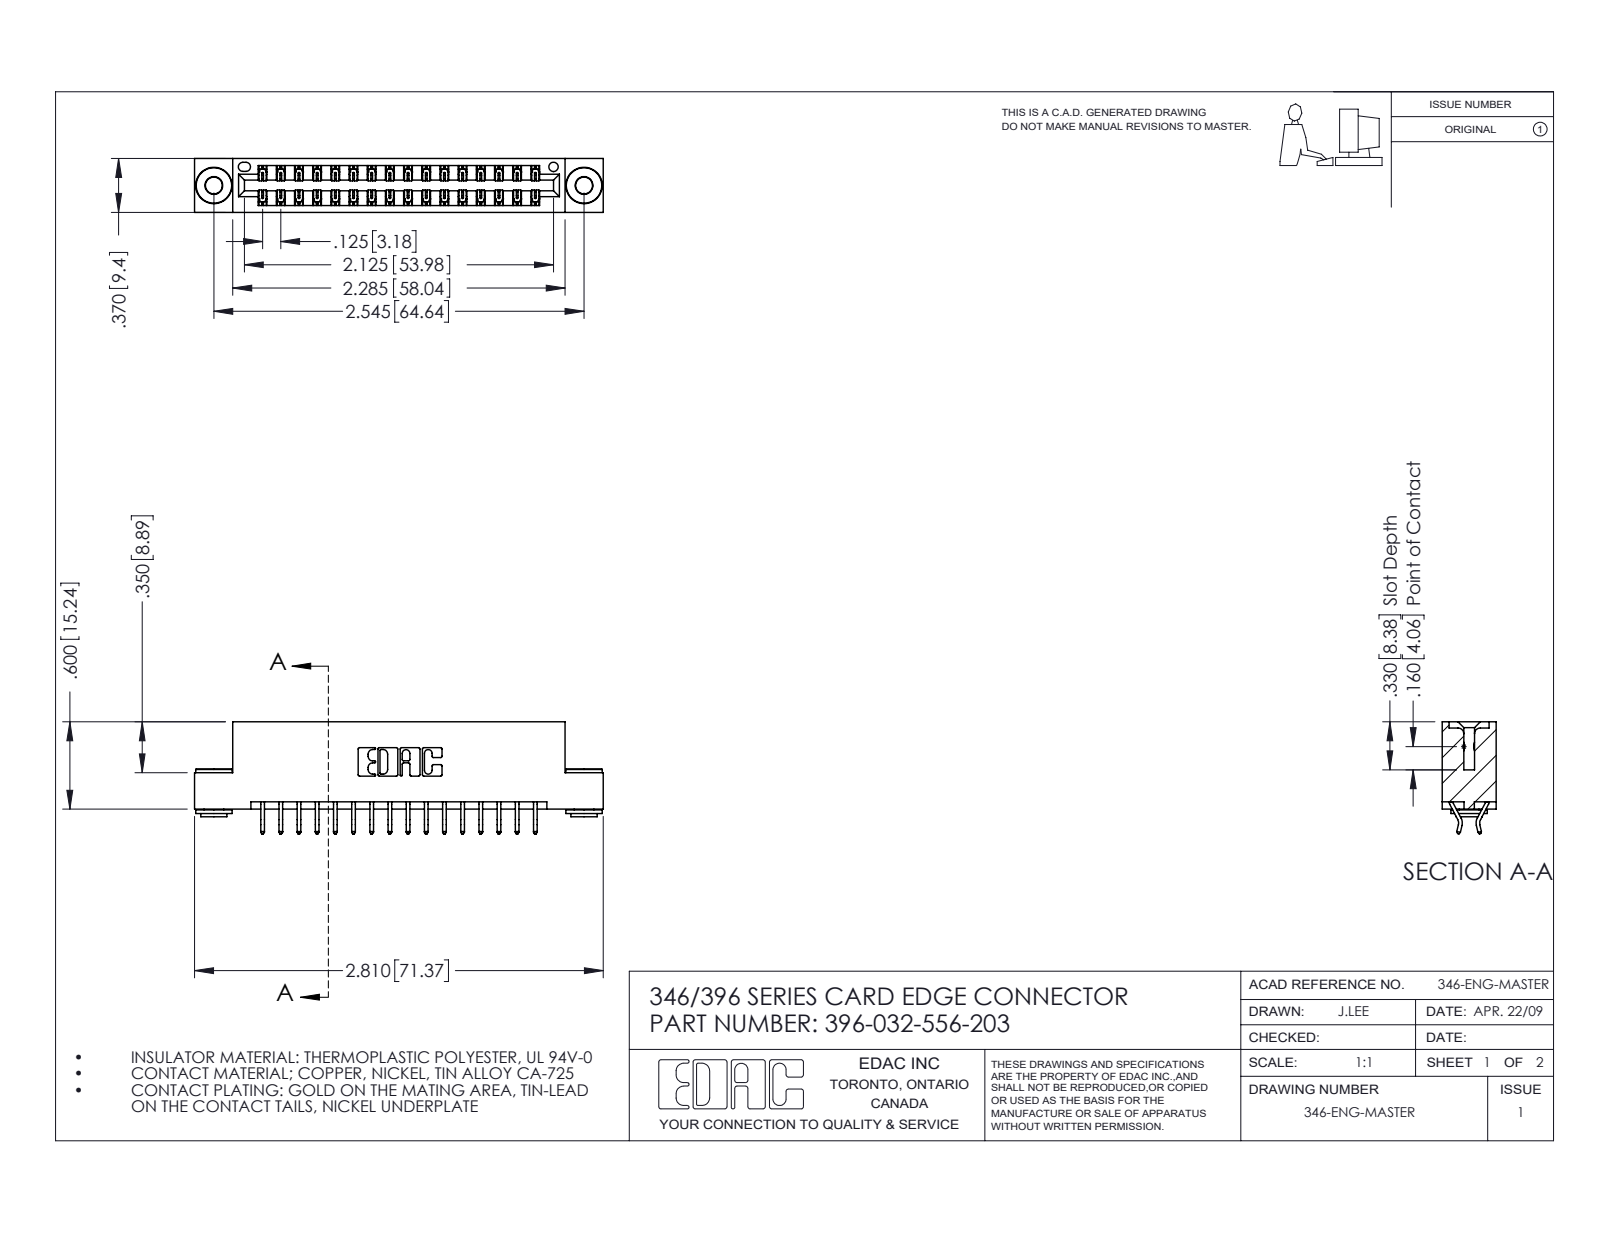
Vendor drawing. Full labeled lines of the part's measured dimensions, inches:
Part name (STEP PRODUCT): 345-292-001_556 Tail; 345-250-002_345-250-002-102; 396-032-556-203; 346 Part_Flush Mounting Lugs - 0.156 Dia-TH
STEP written by: SolidWorks 2016 (CONFIG_CONTROL_DESIGN)
Units: inches
Bodies: 35 solids, 2016 faces (1334 planar, 674 cylindrical, 8 other)
Overall size (bounding box): 2.81 × 0.77 × 0.37
Volume: 0.413 in³ · Surface area: 14.09 in²
Round holes (diameter × count): ⌀0.116 ×2, ⌀0.156 ×2, ⌀0.064 ×1
Round bosses / shafts (diameter × count): ⌀0.25 ×2, ⌀0.18 ×2, ⌀0.136 ×2
Partial cylindrical surfaces — rounded edges, fillets, slot ends (radius × count): R0.006 ×48, R0.01 ×22, R0.007 ×6, R0.031 ×6, R0.026 ×3, R0.01 ×2, R0.014 ×2, R0.022 ×2
Main face-to-face distances: 0.048, 0.322, 0.25, 0.37, 0.025, 0.072, 0.298, 0.275, 0.148, 0.222
Hole centre spacings: 0.246, 2.338, 2.545
